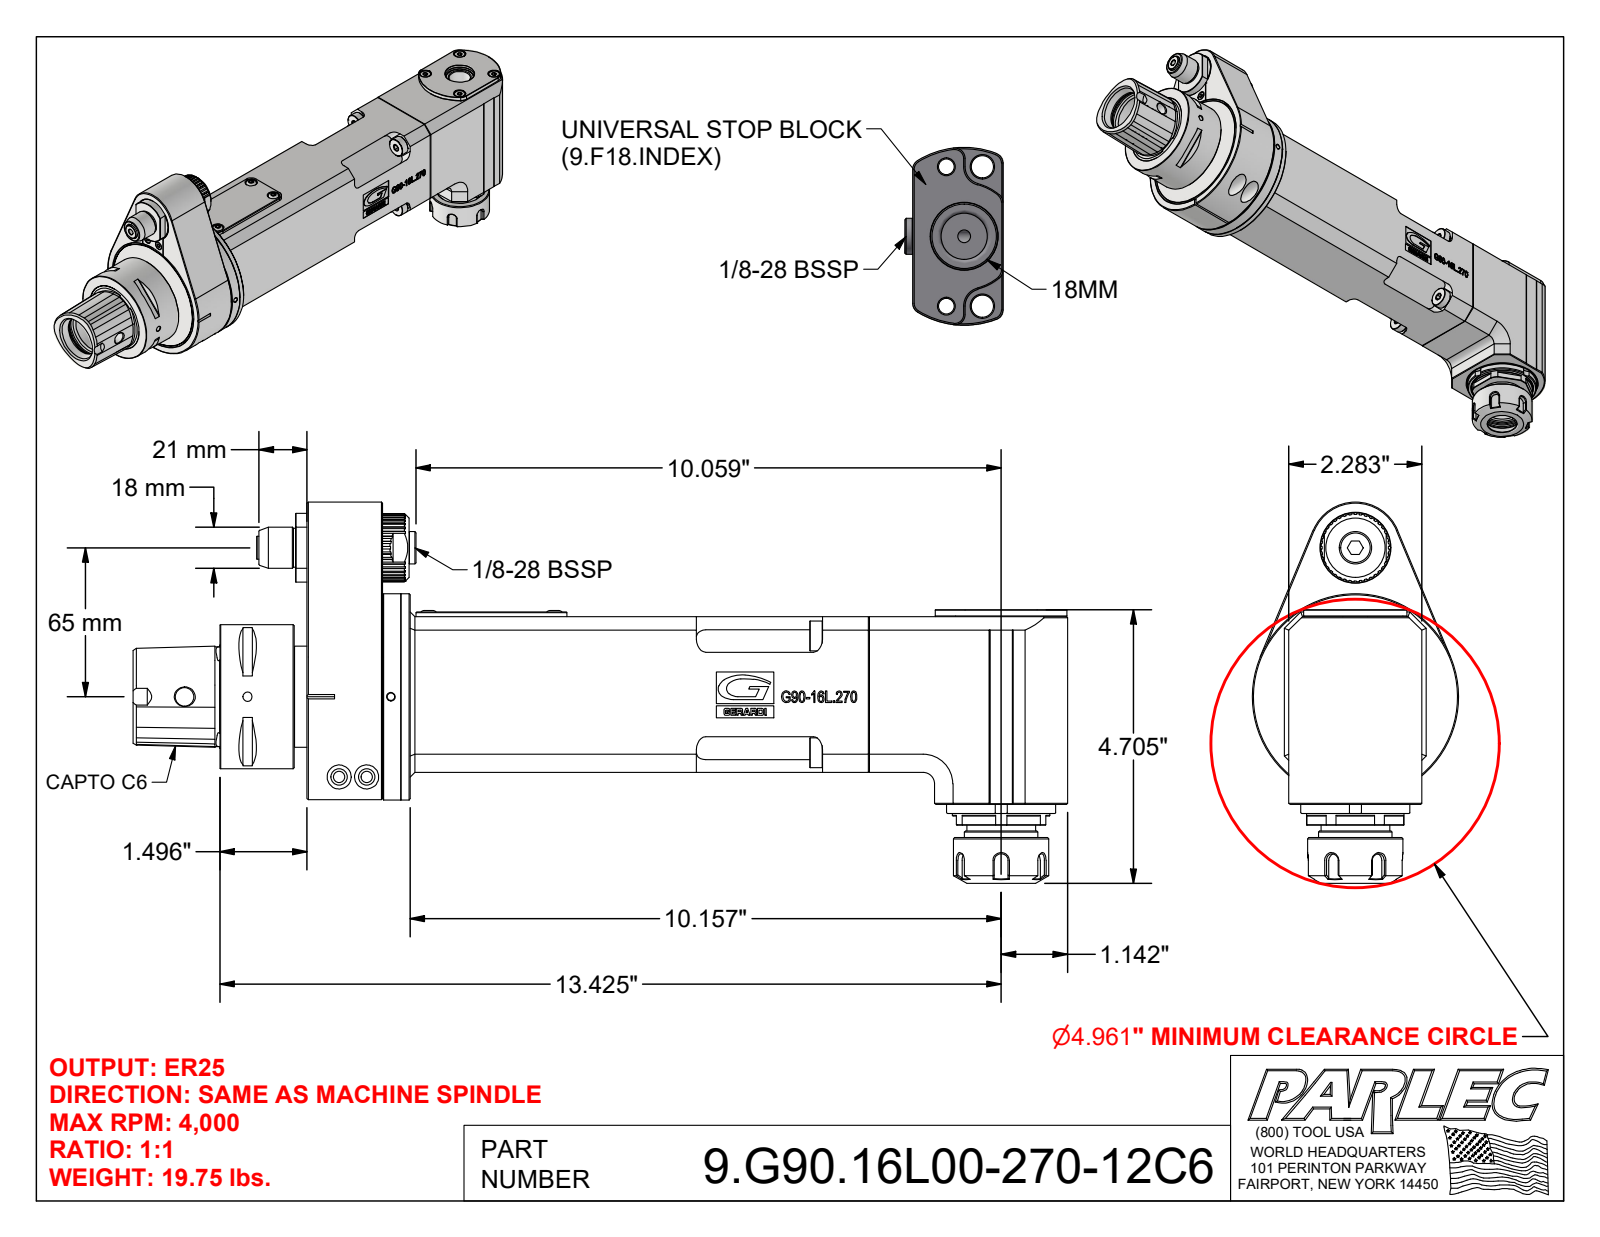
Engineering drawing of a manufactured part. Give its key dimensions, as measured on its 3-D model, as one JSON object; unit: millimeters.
{"part_name": "9.G90.16L00-270-12C6; G90-16L-270; 9_GA1_666_1 (Classic, Type 1, Capto C6, 65mm)", "step_written_by": "Autodesk Inventor 2022 (AUTOMOTIVE_DESIGN)", "units": "millimeters", "bodies": {"solids": 22, "faces": 1512, "planar": 740, "cylindrical": 260, "other": 512}, "overall_size": [408, 166.5, 90], "volume_mm3": 1141000, "surface_area_mm2": 254900, "round_holes": [[5, 8], [3.3, 6], [8.5, 6], [8, 5], [4, 4], [4.2, 4], [6, 3], [7, 2], [10.5, 2], [18, 2], [30.5, 2], [32, 2]], "round_bosses_or_shafts": [[13, 4], [7.8, 4], [7.6, 4], [30, 2], [90, 1], [82, 1], [78, 1], [63, 1]], "partial_cylinders_radius": [[4, 16], [3, 7], [5, 6], [2.5, 5], [6, 4], [2.2, 2], [3.8, 2], [2, 1]], "face_to_face_distances": [58, 68, 33, 3, 8, 5, 1, 9, 71, 79.2], "hole_center_spacings": [17.2, 35.3, 37.5, 64.9, 14, 19.8, 24, 33.9]}
